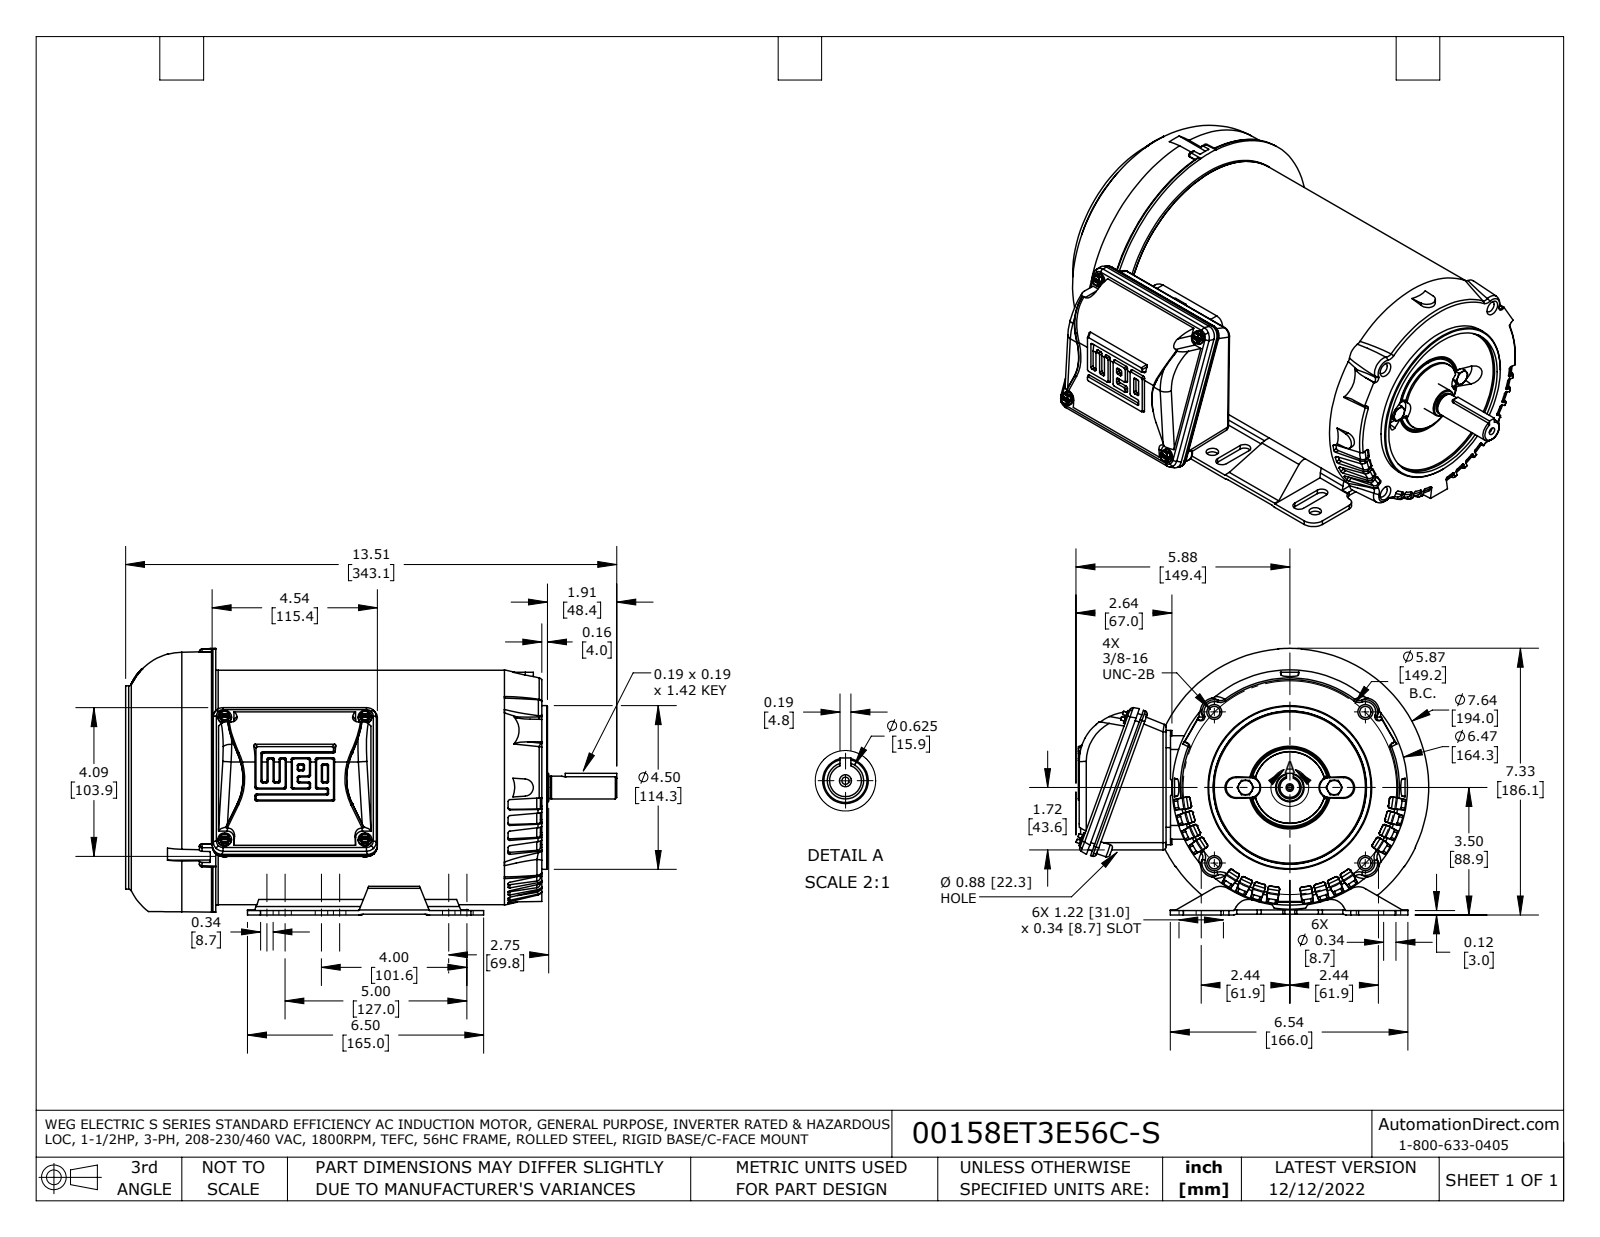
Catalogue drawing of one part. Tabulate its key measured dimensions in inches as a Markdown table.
| quantity | value |
| --- | --- |
| part name | 56HC_3PH_TEFC_GP_13504 broken base surfs w1PHNB 1 fxt |
| STEP written by | SolidWorks 2021 (AUTOMOTIVE_DESIGN) |
| units | inches |
| bodies | 14 solids, 1479 faces (552 planar, 352 cylindrical, 575 other) |
| overall size | 13.508 × 9.7 × 7.551 |
| volume | 425.4 in³ |
| surface area | 721.3 in² |
| round holes (diameter × count) | 0.343 × 6, 0.313 × 4, 0.124 × 1 |
| round bosses / shafts (diameter × count) | 0.374 × 4, 0.35 × 2, 6.447 × 1, 6.447 × 1, 5.591 × 1, 4.5 × 1, 0.783 × 1, 0.625 × 1 |
| partial cylindrical surfaces (radius × count) | 0.047 × 40, 0.006 × 38, 0.051 × 32, 0.059 × 12, 0.087 × 12, 0.171 × 12, 0.02 × 10, 0.079 × 8 |
| main face-to-face distances | 7.874, 0.12, 0.067, 7.941, 2.283, 2.35, 10.224, 11.248, 8.965, 8.898 |
| hole center spacings | 2.937, 4.154, 5.5, 1, 4, 5, 5.59, 5.874 |
